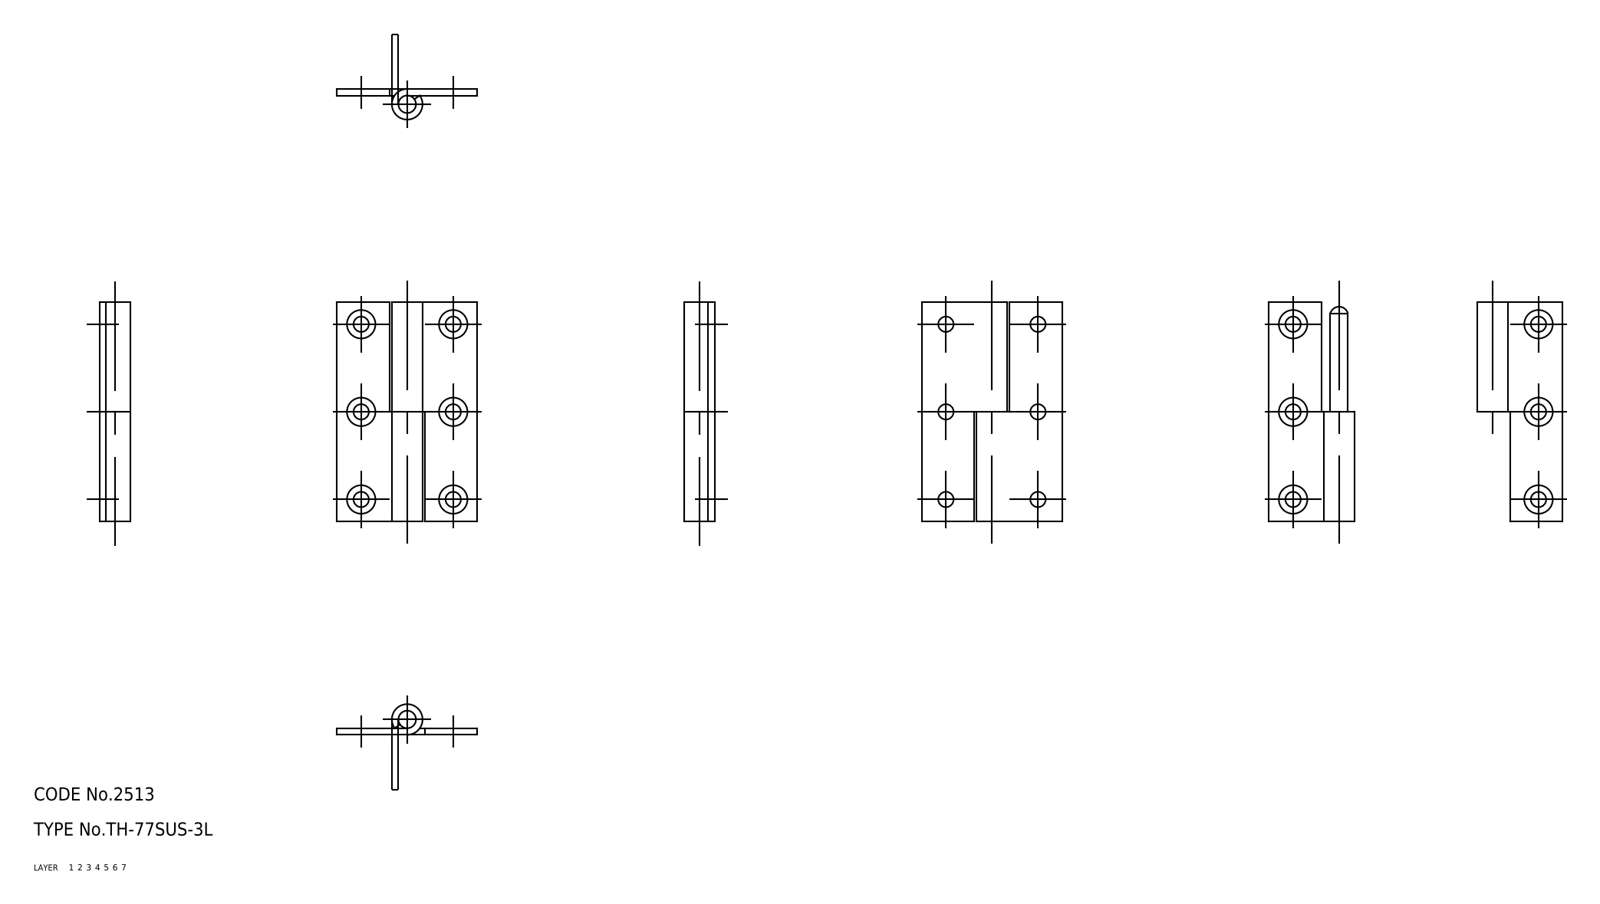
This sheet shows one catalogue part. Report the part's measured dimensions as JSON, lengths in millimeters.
{"part_name": "shaft; hinge piece_B; hinge piece_A; TH_77SUS_3L_16413_36", "step_written_by": "CADfix (AUTOMOTIVE_DESIGN)", "units": "millimeters", "bodies": {"solids": 3, "faces": 36, "planar": 0, "cylindrical": 0, "other": 36}, "overall_size": [50, 32, 7], "volume_mm3": 3621, "surface_area_mm2": 5315}
